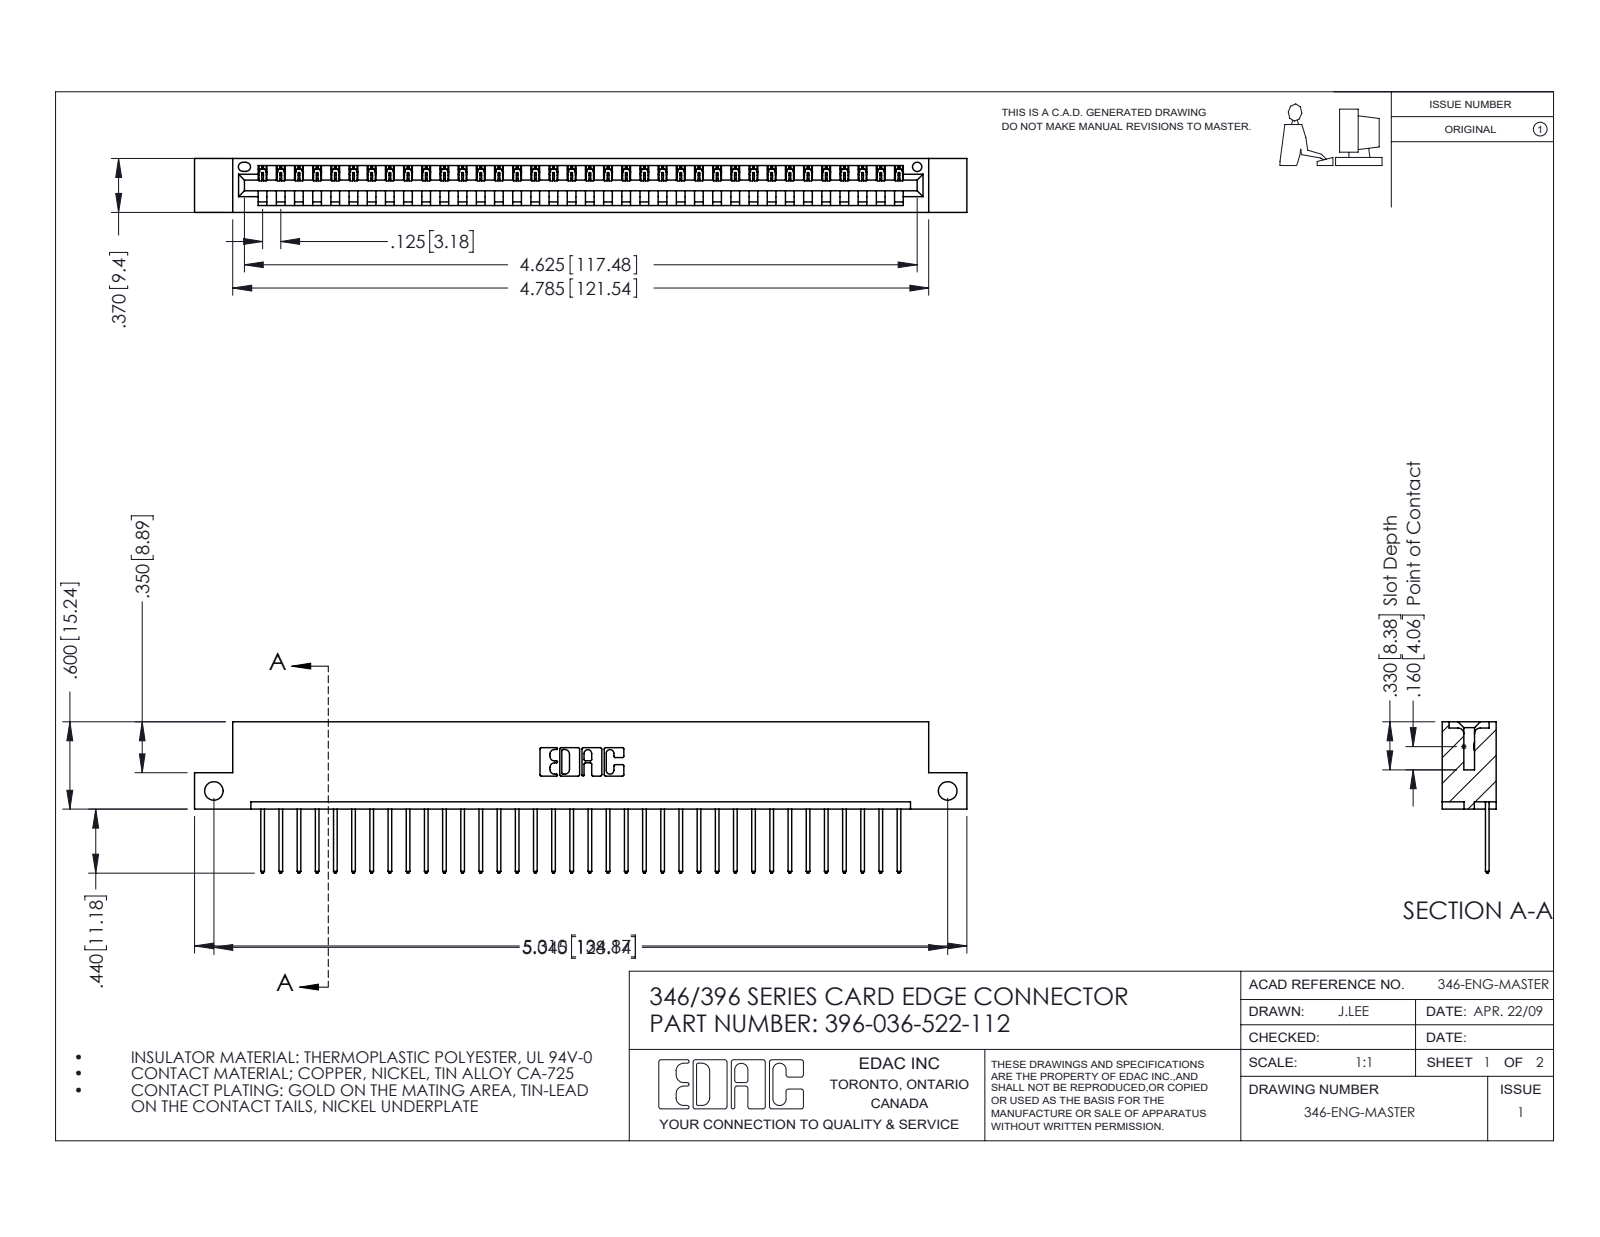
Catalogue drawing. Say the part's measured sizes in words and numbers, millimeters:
The part is named "396-036-522-112; 345-292-001_345-293-122; 346 Part_Flush Mounting Lugs - Side Mount". Its 3-D file was written by "SolidWorks 2016 (CONFIG_CONTROL_DESIGN)". It is 37 solids with 2210 faces: 1516 planar, 694 cylindrical and 0 other. Overall it measures 134.9 by 26.4 by 9.4 millimeters. Its volume is 12 800 cubic millimeters and its surface area 15 900 square millimeters. Round holes: 2 of diameter 3.3, 1 of diameter 1.6. Partial cylindrical surfaces (rounded edges, fillets, slot ends): 72 of radius 0.2, 72 of radius 0.3, 22 of radius 0.3, 6 of radius 0.2, 6 of radius 0.8, 3 of radius 0.7, 2 of radius 0.8, 2 of radius 1. The main face-to-face distances are 1.2, 8.2, 9.4, 6.4, 1.8, 7.6, 0.6, 3.8, 5.6, 2.5. The hole center spacings are 128.1.
